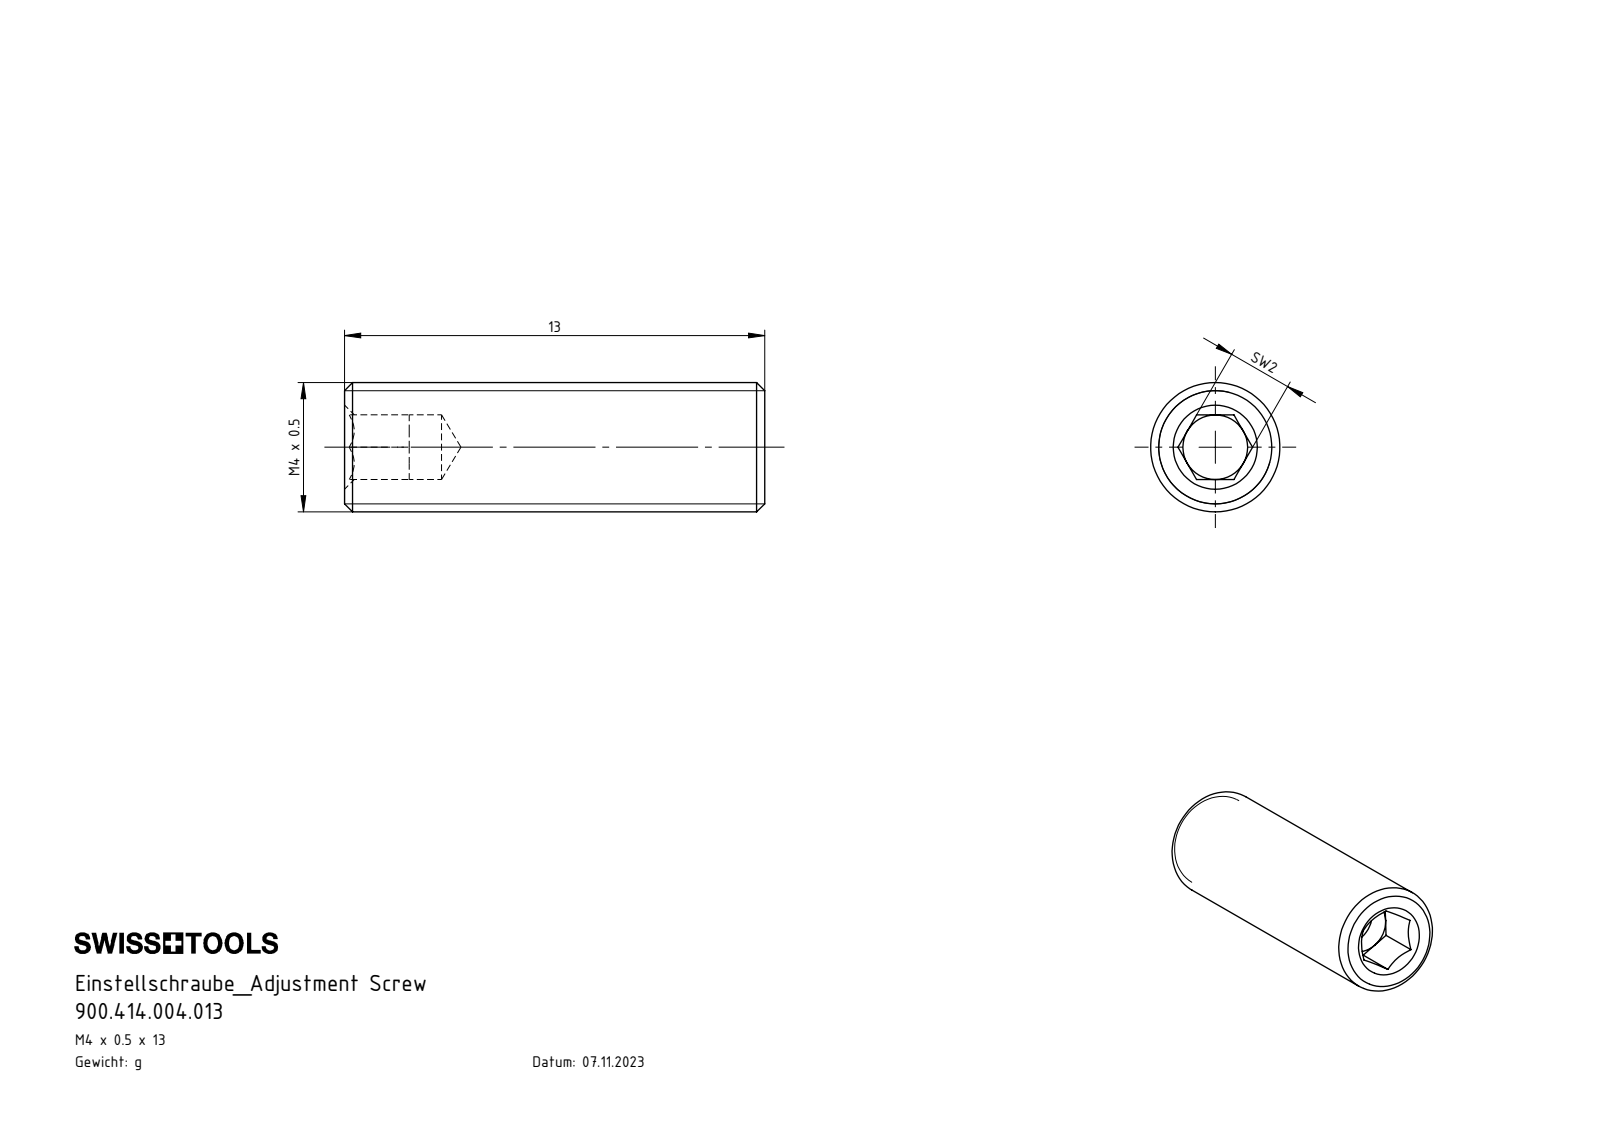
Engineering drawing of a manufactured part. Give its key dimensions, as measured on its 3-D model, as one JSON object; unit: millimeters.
{"part_name": "900.414.004.013", "step_written_by": "SolidWorks 2022 (AUTOMOTIVE_DESIGN)", "units": "millimeters", "bodies": {"solids": 1, "faces": 26, "planar": 14, "cylindrical": 4, "other": 8}, "overall_size": [13, 4, 4], "volume_mm3": 152, "surface_area_mm2": 204, "round_holes": [[2, 1]], "round_bosses_or_shafts": [[4, 1]], "face_to_face_distances": [2, 13, 11]}
